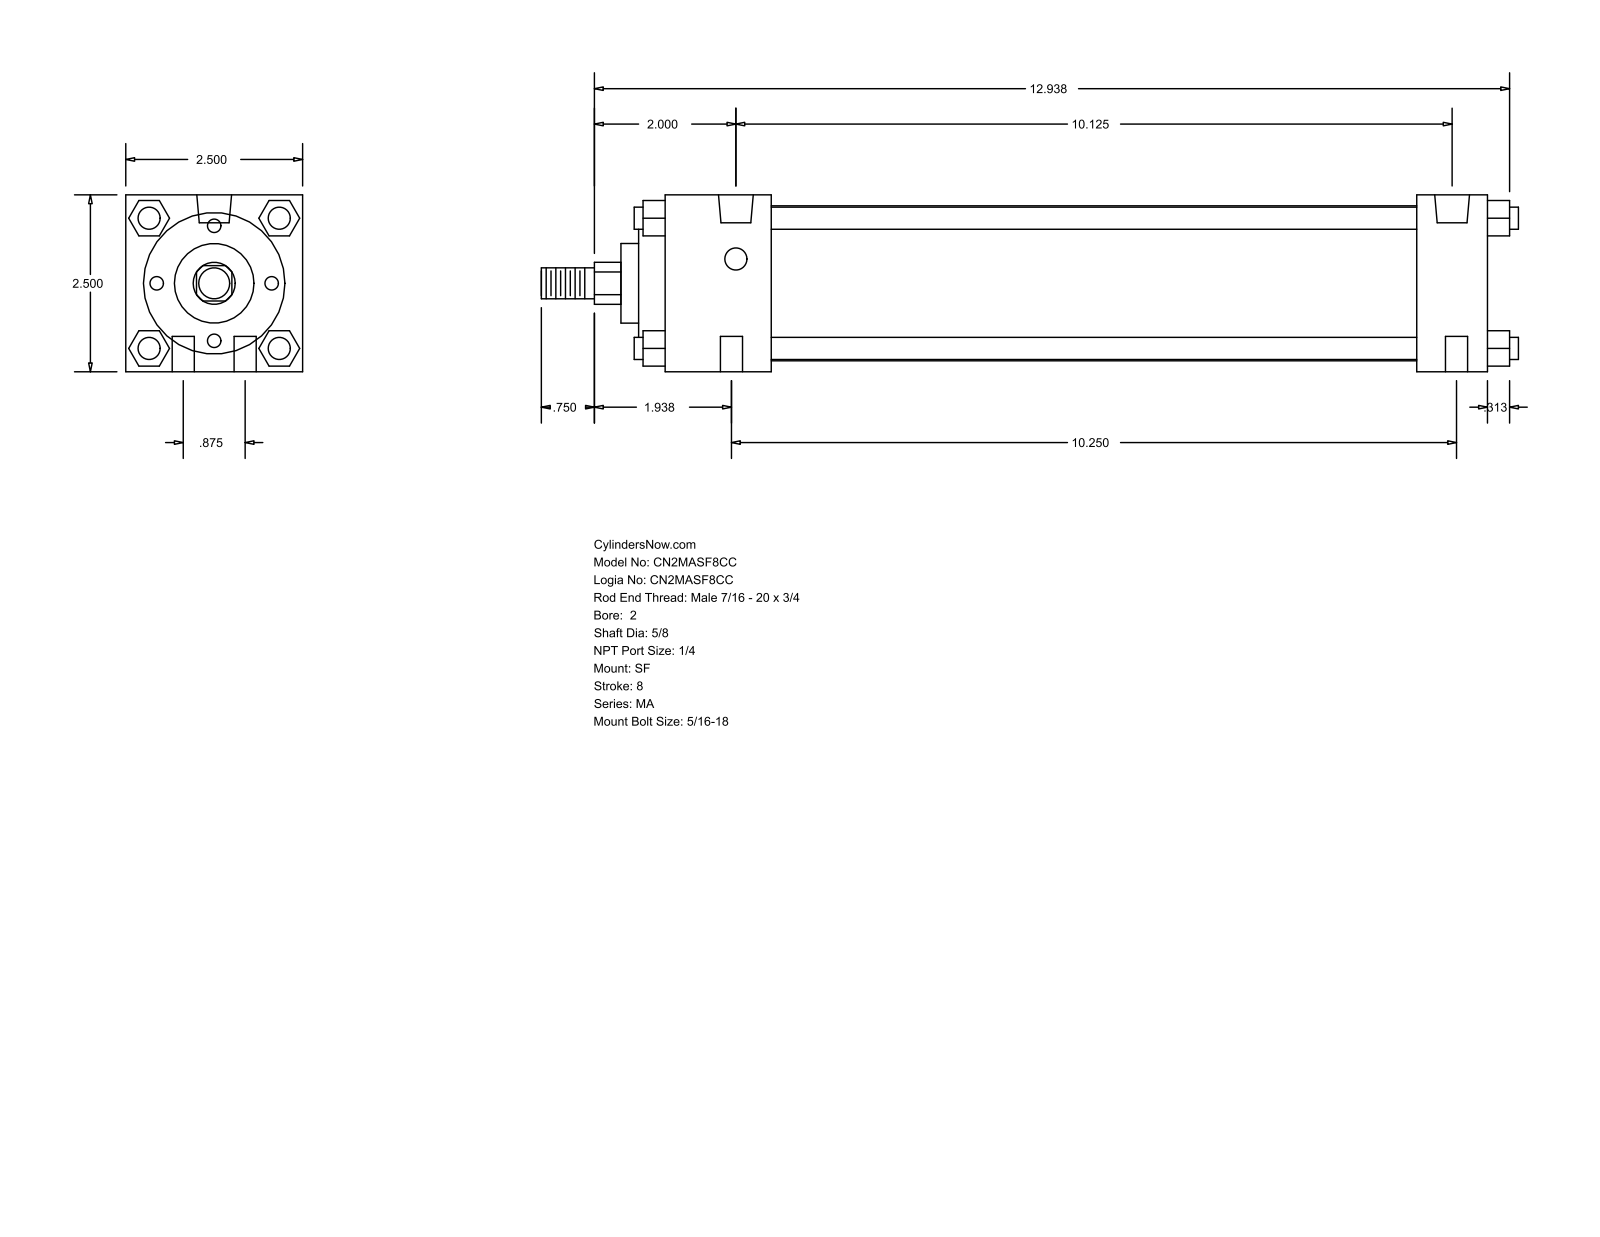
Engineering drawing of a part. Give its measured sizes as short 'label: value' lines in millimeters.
name: MA_SF__0200_0.625
written by: GSSL Pune (CONFIG_CONTROL_DESIGN)
unit: mm
bodies: 0 solids, 126 faces (95 planar, 31 cylindrical, 0 other)
size: 350.84 × 63.5 × 63.5
holes: 6× ⌀7.94, 2× ⌀12.49
bosses: 4× ⌀7.94, 1× ⌀55.63, 1× ⌀50.8, 1× ⌀28.57, 1× ⌀15.88, 1× ⌀11.11
rounds: 1× R7.54
face distances: 63.5, 12.7, 38.1, 295.28, 269.87, 25.41, 231.77, 257.18, 9.52, 47.62
hole spacings: 11.22, 22.22, 257.18, 259, 259.01, 260.35, 261.3
